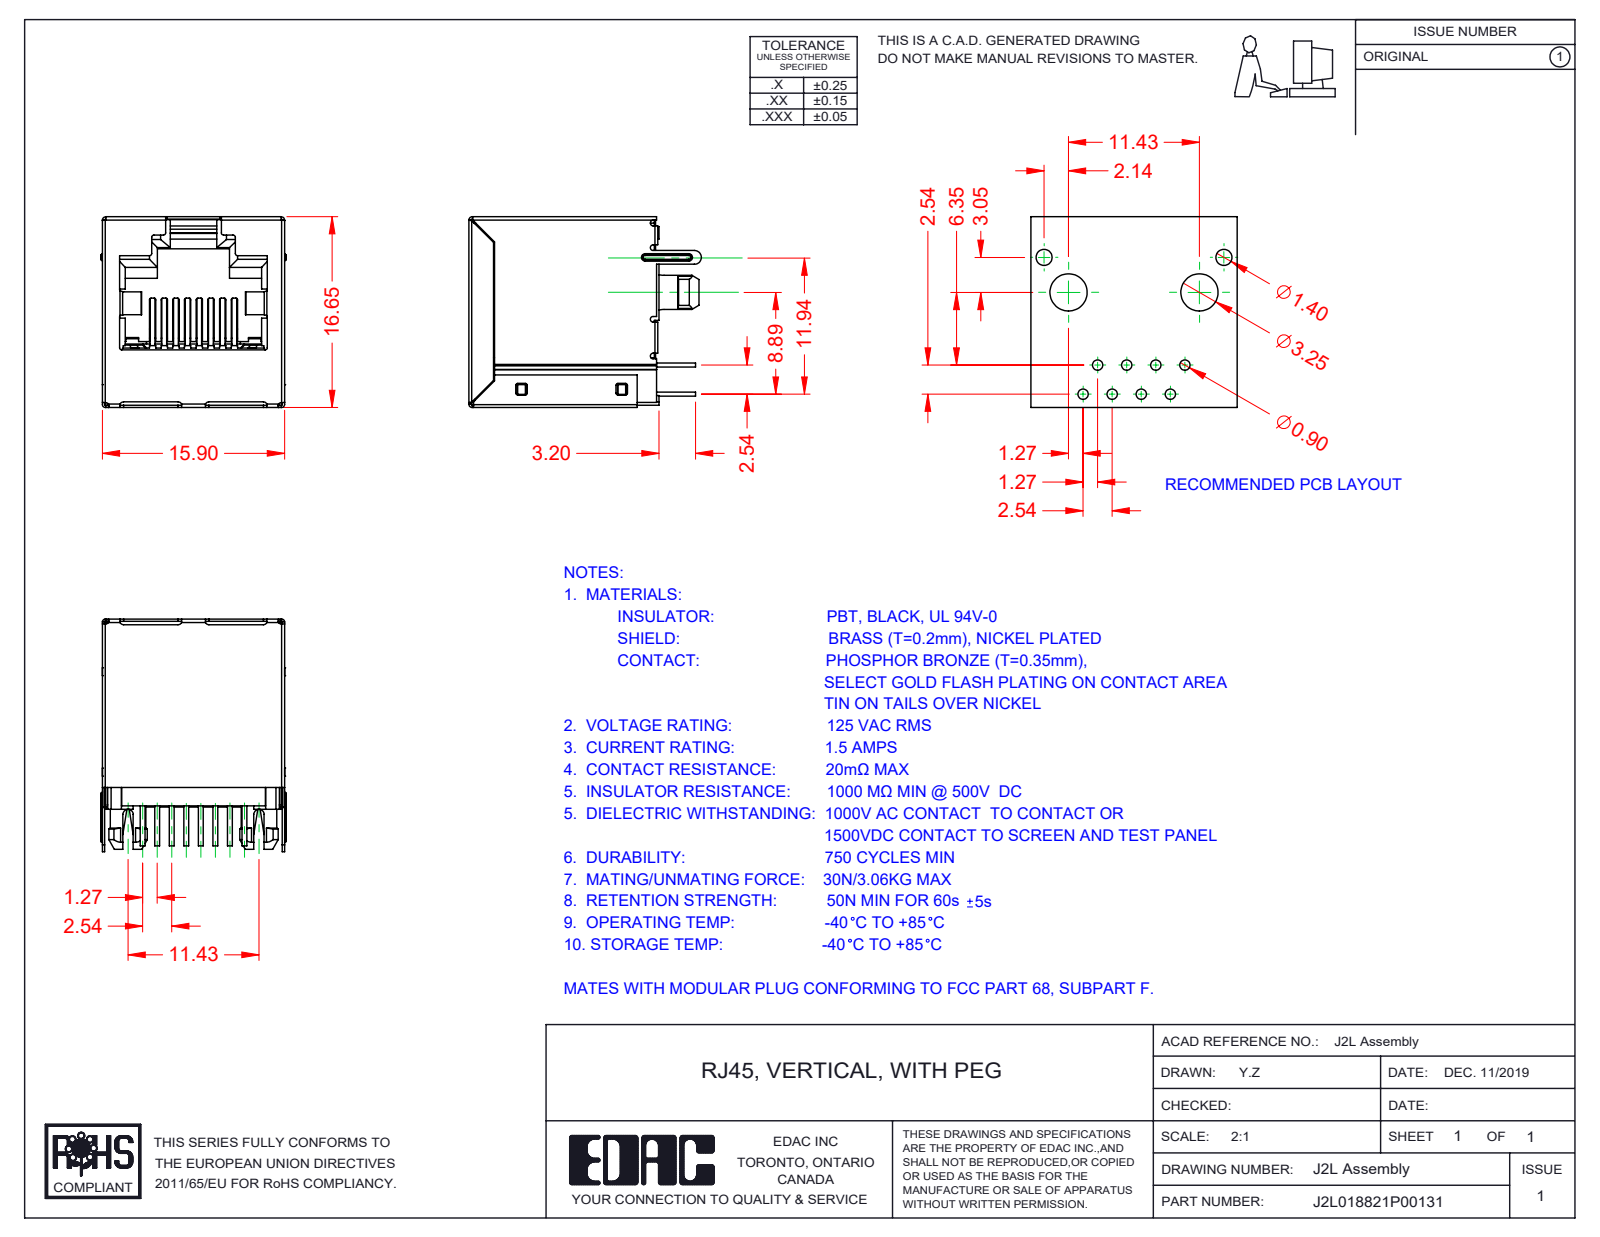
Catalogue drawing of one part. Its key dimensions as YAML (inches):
part_name: "2L Contacts; 2L Insulator; RJ2L018821P00131; 2L Shield (+1 more)"
step_written_by: "SolidWorks 2016 (CONFIG_CONTROL_DESIGN)"
units: inches
bodies: {solids: 11, faces: 1125, planar: 778, cylindrical: 284, other: 63}
overall_size: [0.799, 0.656, 0.638]
volume: 0.166
surface_area: 10.03
round_bosses_or_shafts:
  - {diameter: 0.122, count: 2}
  - {diameter: 0.043, count: 2}
partial_cylinders:
  - {radius: 0.006, count: 64}
  - {radius: 0.01, count: 20}
  - {radius: 0.008, count: 16}
  - {radius: 0.012, count: 14}
  - {radius: 0.014, count: 9}
  - {radius: 0.004, count: 8}
  - {radius: 0.011, count: 4}
  - {radius: 0.02, count: 3}
face_to_face_distances: [0.608, 0.618, 0.648, 0.638, 0.646, 0.616, 0.64, 0.626, 0.61, 0.047]
